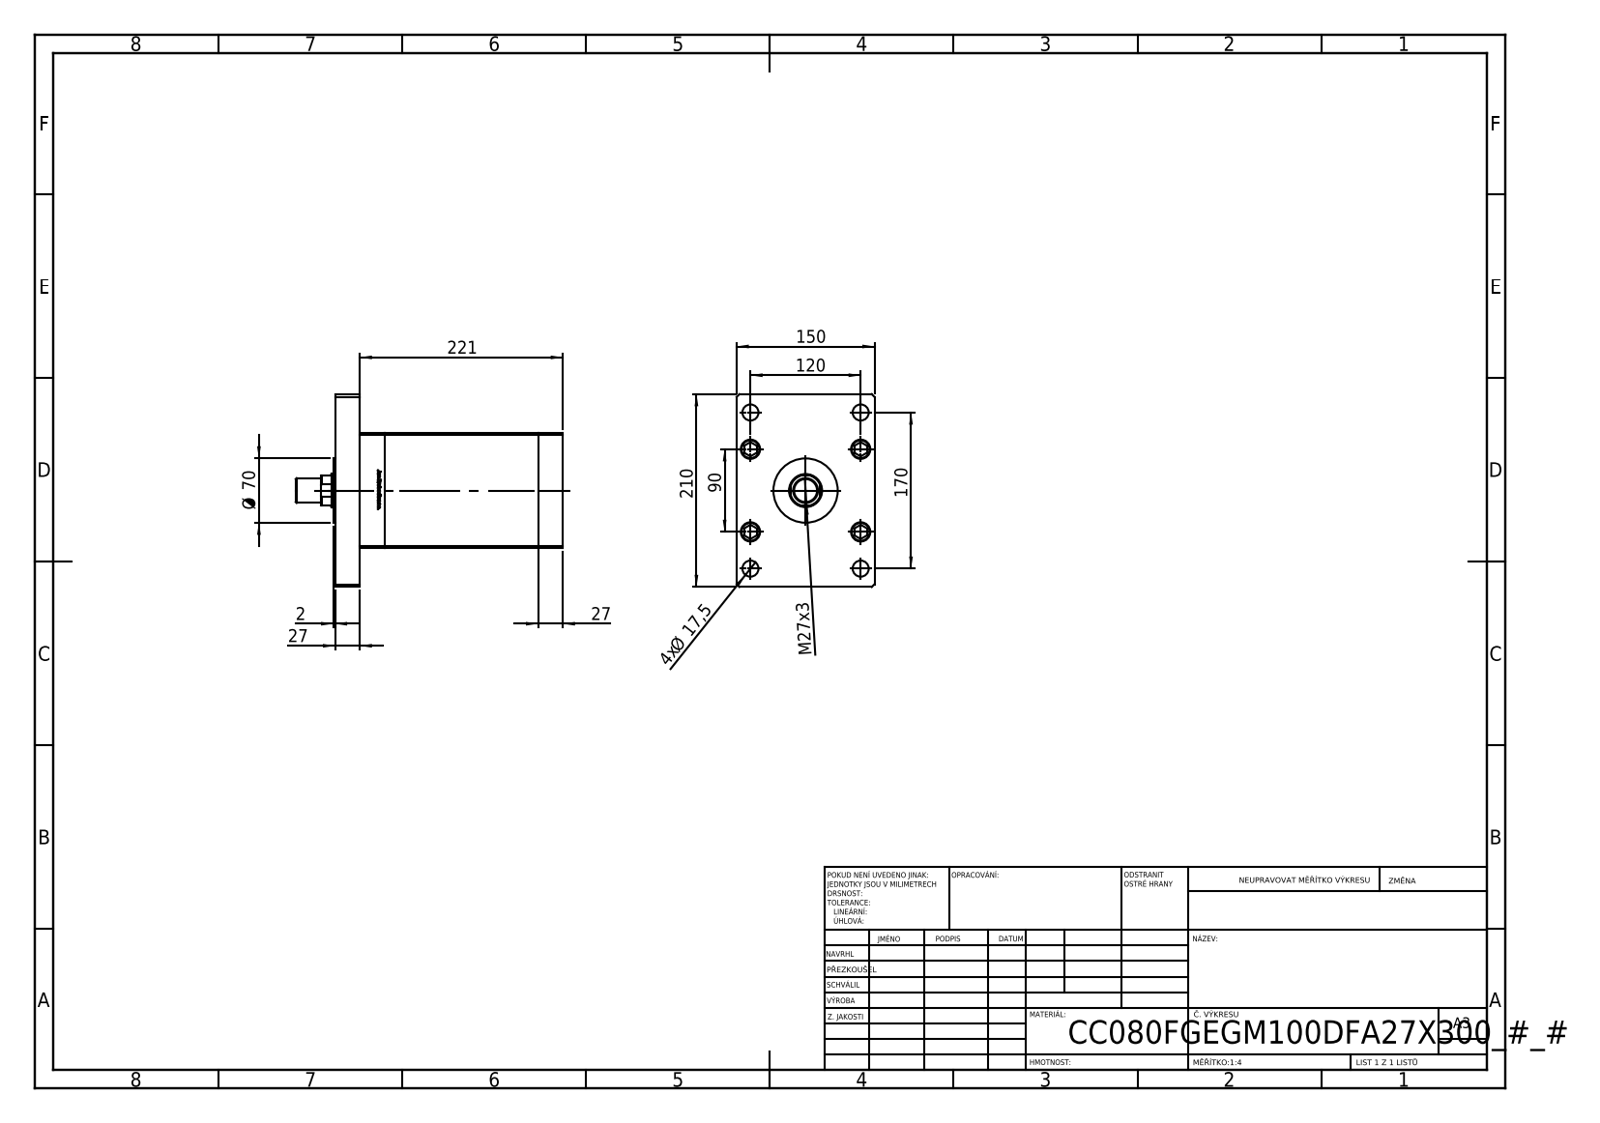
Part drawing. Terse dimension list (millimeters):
name: V220C_F; V220C BACK_F; V220C_F_MIDDLE; FEMALE_PART_FOR_DFA (+3 more)
written by: SolidWorks 2019 (CONFIG_CONTROL_DESIGN)
unit: mm
bodies: 20 solids, 1343 faces (529 planar, 196 cylindrical, 618 other)
size: 290.8 × 210 × 150
volume: 4 413 000 mm³; area: 484 407 mm²
holes: 9× ⌀17.5, 5× ⌀22, 4× ⌀16, 4× ⌀21, 2× ⌀2, 2× ⌀13.16, 1× ⌀25.5, 1× ⌀36, 1× ⌀37.5
bosses: 9× ⌀8, 5× ⌀21, 1× ⌀80, 1× ⌀70, 1× ⌀44, 1× ⌀27, 1× ⌀25
rounds: 2× R0.93, 1× R9.5, 1× R15, 1× R17.5
face distances: 27, 194, 221, 150, 125, 167, 54, 248, 33.5, 6.5
hole spacings: 51, 40, 75, 104.04, 120, 126.49, 130, 176.92
